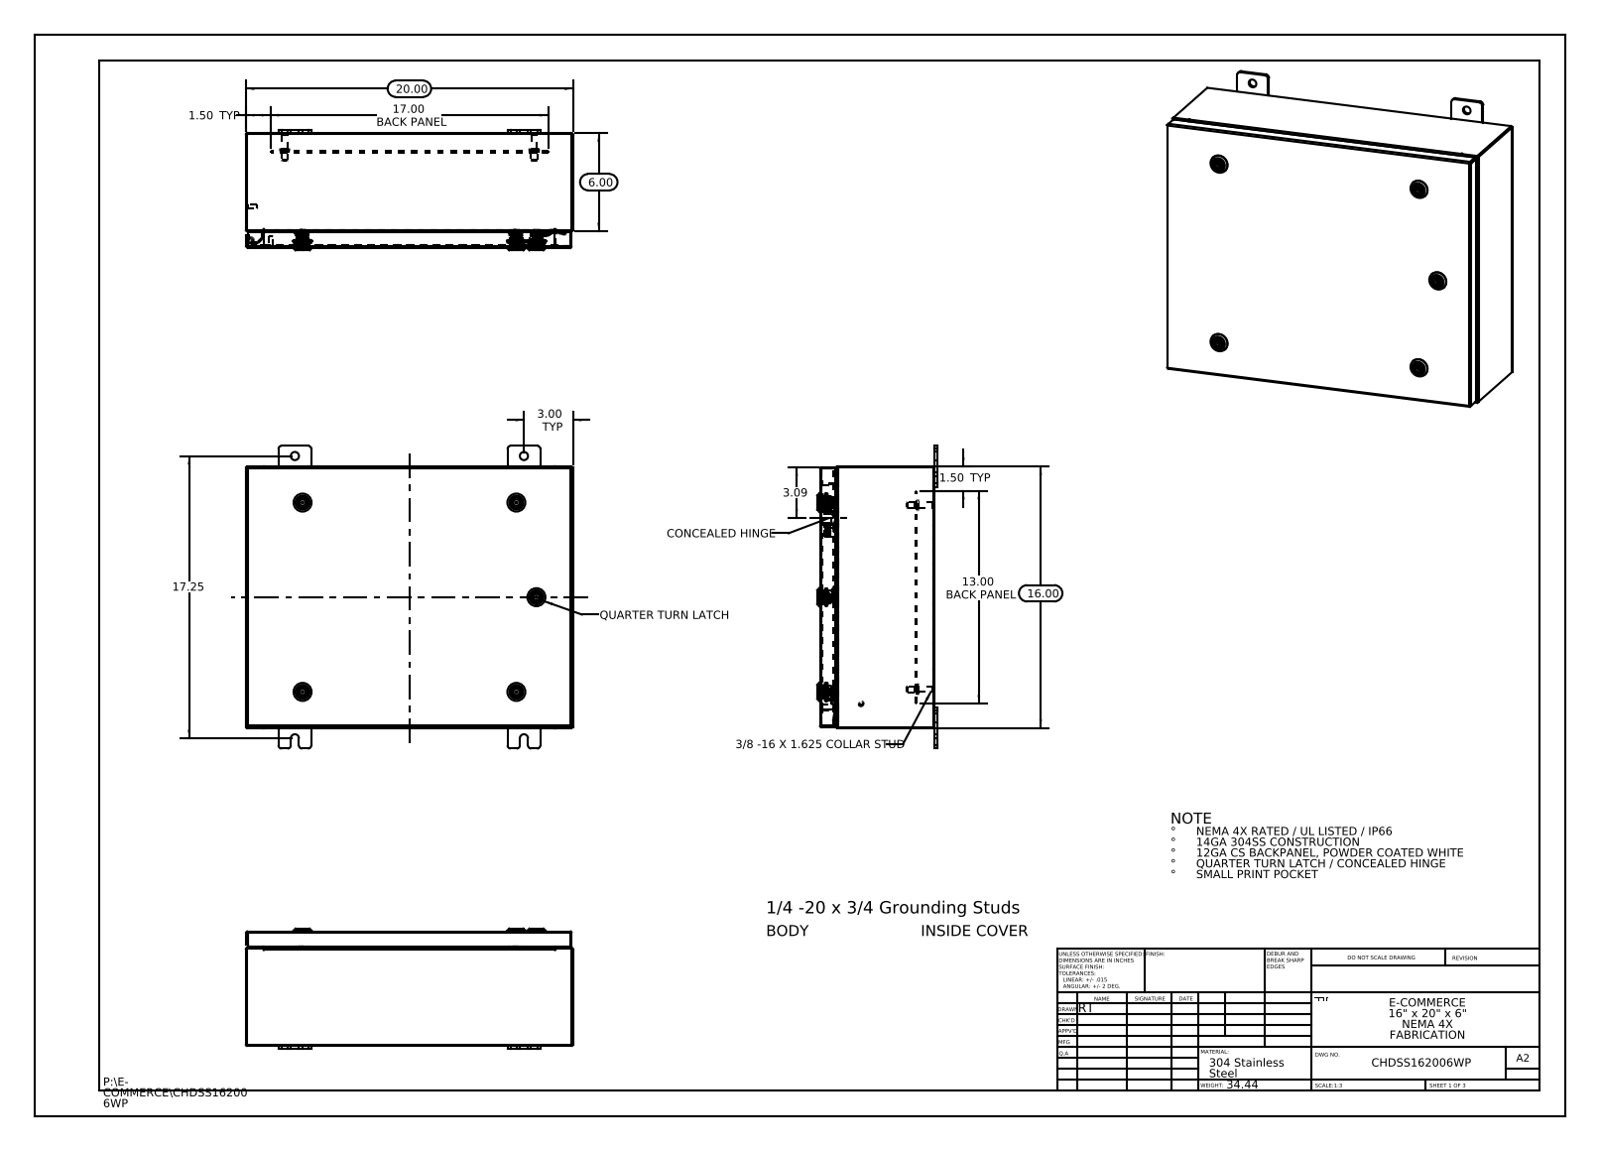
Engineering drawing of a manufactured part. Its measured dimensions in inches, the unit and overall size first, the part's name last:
Units: inches
Overall size (bounding box): 20 × 18.5 × 7.356
Round holes (diameter × count): ⌀0.5 ×8, ⌀0.197 ×5, ⌀0.394 ×5, ⌀0.4 ×5, ⌀0.63 ×5, ⌀0.787 ×5, ⌀0.136 ×2, ⌀0.211 ×1
Round bosses / shafts (diameter × count): ⌀0.236 ×7, ⌀1.102 ×5, ⌀0.78 ×5, ⌀0.626 ×5, ⌀0.61 ×5, ⌀0.531 ×5, ⌀0.392 ×5, ⌀0.114 ×5
Partial cylindrical surfaces — rounded edges, fillets, slot ends (radius × count): R0.006 ×165, R0.118 ×165, R0.028 ×60, R0.19 ×24, R0.02 ×20, R0.197 ×20, R0.013 ×18, R0.088 ×18
Main face-to-face distances: 0.075, 0.074, 7.01, 6.935, 6.936, 6.861, 15.925, 1, 1.075, 5.861
Hole centre spacings: 1.858, 3.065, 5.627, 11.25, 11.569, 13.015, 13.069, 13.164
Volume: 123.9 in³ · Surface area: 3 105 in²
Bodies: 47 solids, 4538 faces (1332 planar, 1416 cylindrical, 1790 other)
Part name (STEP PRODUCT): Concealed Hinge enclosure side; Quarter-20 CD Stud; Nut-211301-IB-Industrilas_Nut-211301-IB-Industrilas; Insert-221320-IB-Industrilas_Insert-221320-IB-Industrilas (+8 more)
STEP written by: SolidWorks 2013 (CONFIG_CONTROL_DESIGN)
